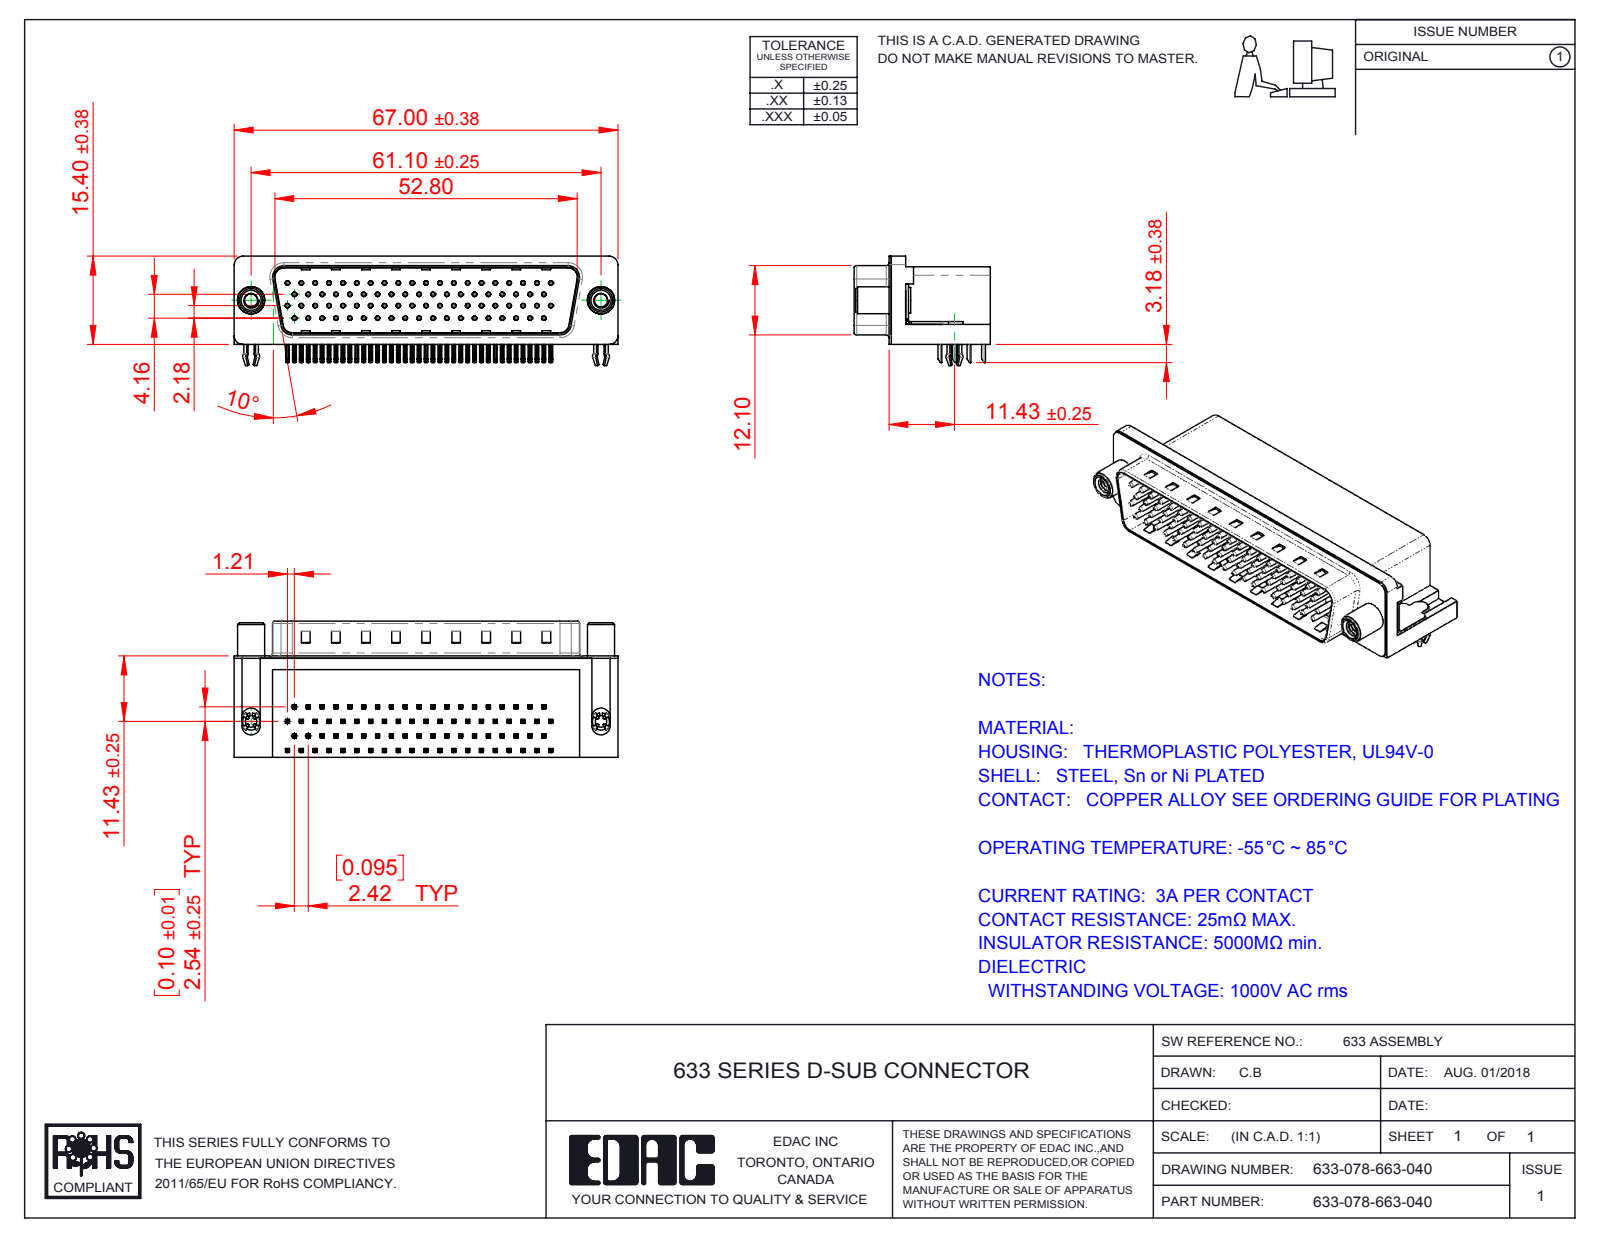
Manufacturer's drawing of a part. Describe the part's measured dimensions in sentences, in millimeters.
The part is named "633 Round Threaded Standoff; 633 4 Prong Board Lock_78 Contact; 633 Contact Middle_78 Contact; 633 Contact Top_78 Contact (+5 more)". Its 3-D file was written by "SolidWorks 2016 (CONFIG_CONTROL_DESIGN)". It is 84 solids with 6390 faces: 4015 planar, 1792 cylindrical and 583 other. Overall it measures 67 by 23.8 by 19.1 millimeters. Its volume is 14 713 cubic millimeters and its surface area 16 628 square millimeters. Round holes: 78 of diameter 0.35, 78 of diameter 0.8, 2 of diameter 2, 2 of diameter 2.3, 2 of diameter 3.1, 2 of diameter 4, 2 of diameter 4.8, 2 of diameter 5. Round bosses or shafts: 78 of diameter 0.75, 2 of diameter 4.9, 2 of diameter 4.7, 2 of diameter 4.5, 2 of diameter 3.85, 2 of diameter 3. Partial cylindrical surfaces (rounded edges, fillets, slot ends): 316 of radius 0.25, 156 of radius 0.12, 16 of radius 1, 9 of radius 0.5, 8 of radius 1.6, 6 of radius 1.5, 4 of radius 0.45, 4 of radius 0.9. The main face-to-face distances are 0.4, 13.2, 17.3, 11.7, 13.35, 2.05, 13.75, 1.65, 1.85, 11.9. The hole center spacings are 2.42, 4.84, 7.26, 9.68, 6.26, 7.13, 12.1, 8.62.
